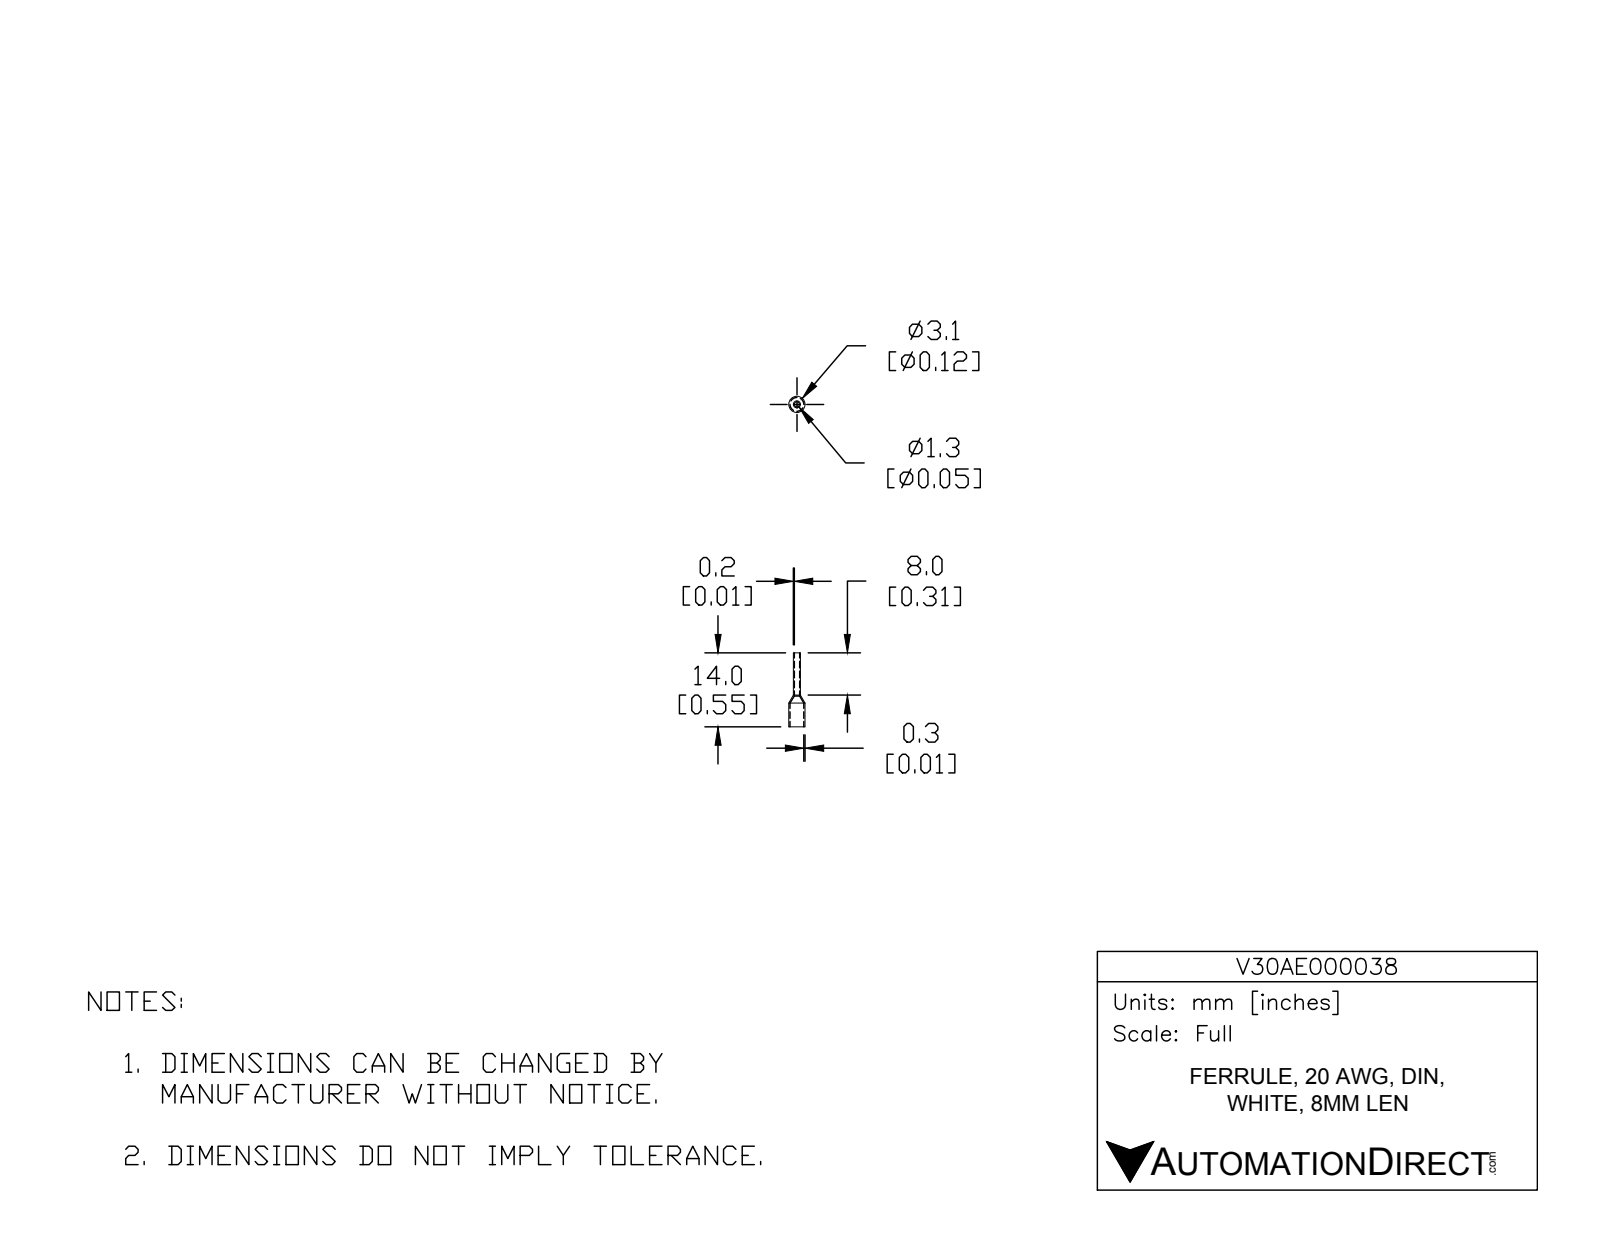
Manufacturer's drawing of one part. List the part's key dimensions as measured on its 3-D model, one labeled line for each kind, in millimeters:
Part name (STEP PRODUCT): V30AE000038
STEP written by: SolidWorks 2017 (AUTOMOTIVE_DESIGN)
Units: millimetres
Bodies: 1 solid, 14 faces (2 planar, 8 cylindrical, 4 other)
Overall size (bounding box): 14 × 3.1 × 3.1
Volume: 17 mm³ · Surface area: 163 mm²
Round holes (diameter × count): ⌀1 ×1, ⌀2.6 ×1
Round bosses / shafts (diameter × count): ⌀3.1 ×1, ⌀1.3 ×1
Main face-to-face distances: 14
